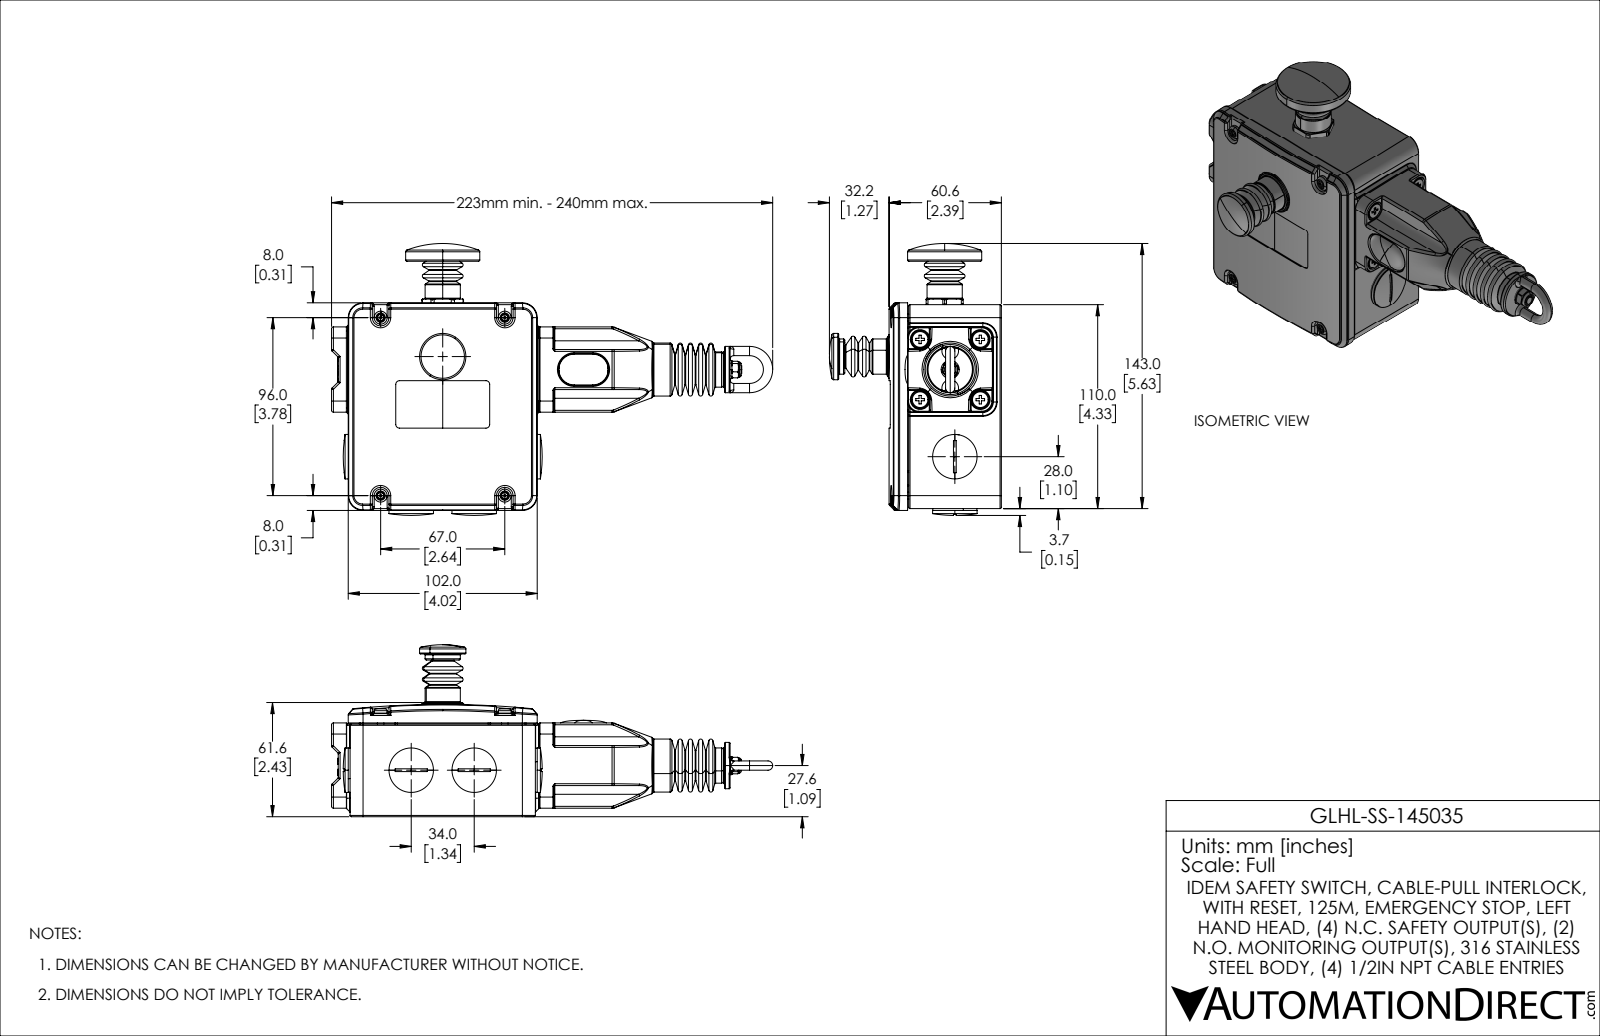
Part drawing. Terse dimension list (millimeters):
name: GLHL-SS-145035
written by: SolidWorks 2021 (AUTOMOTIVE_DESIGN)
unit: mm
bodies: 36 solids, 3678 faces (968 planar, 1195 cylindrical, 1515 other)
size: 238.1 × 146.7 × 92.8
volume: 298 200 mm³; area: 177 800 mm²
holes: 9× ⌀5, 9× ⌀5.3, 8× ⌀9.6, 6× ⌀9, 4× ⌀3.3, 4× ⌀4, 4× ⌀4.1, 4× ⌀4.8, 4× ⌀5.4, 4× ⌀5.8, 3× ⌀3, 3× ⌀4.4
bosses: 11× ⌀5, 8× ⌀8.5, 8× ⌀4.4, 5× ⌀7, 4× ⌀20, 4× ⌀3.5, 4× ⌀1.3, 3× ⌀24
rounds: 206× R0.5, 159× R1, 64× R0.2, 48× R0.7, 14× R0.2, 14× R2, 12× R0.3, 8× R0.1
face distances: 1, 2, 3.5, 55.4, 52.5, 2.9, 102, 4, 110, 8.5
hole spacings: 32.5, 32.5, 23, 9.5, 22.9, 23, 23, 32.5
